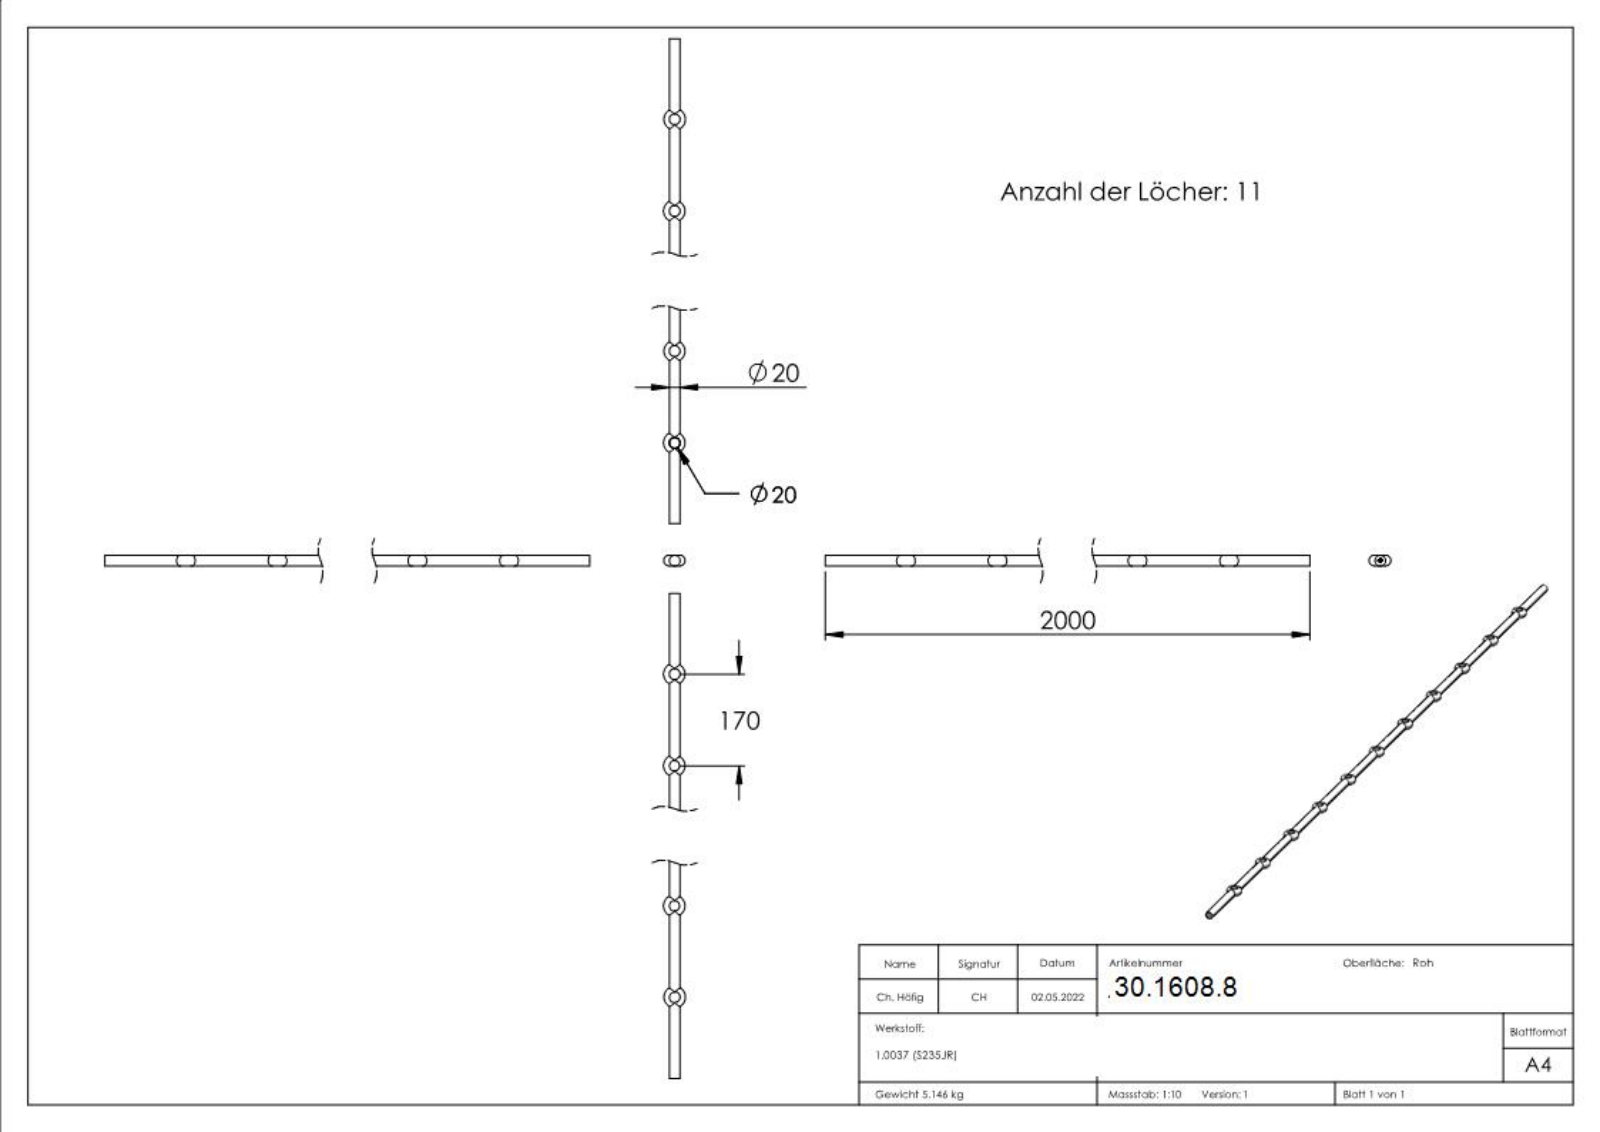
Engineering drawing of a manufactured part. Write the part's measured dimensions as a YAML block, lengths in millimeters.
part_name: "42-4"
step_written_by: "SolidWorks 2018 (CONFIG_CONTROL_DESIGN)"
units: millimeters
bodies: {solids: 1, faces: 251, planar: 132, cylindrical: 23, other: 96}
overall_size: [2000, 40, 20]
volume: 659899
surface_area: 145924
round_holes:
  - {diameter: 20, count: 11}
round_bosses_or_shafts:
  - {diameter: 20, count: 1}
face_to_face_distances: [2000, 1999.9, 4.5, 0.41, 1.14, 1.82, 2.9, 3.27, 0.34, 2.28]
hole_center_spacings: [170, 340, 510, 680, 850, 1020, 1190, 1360]
